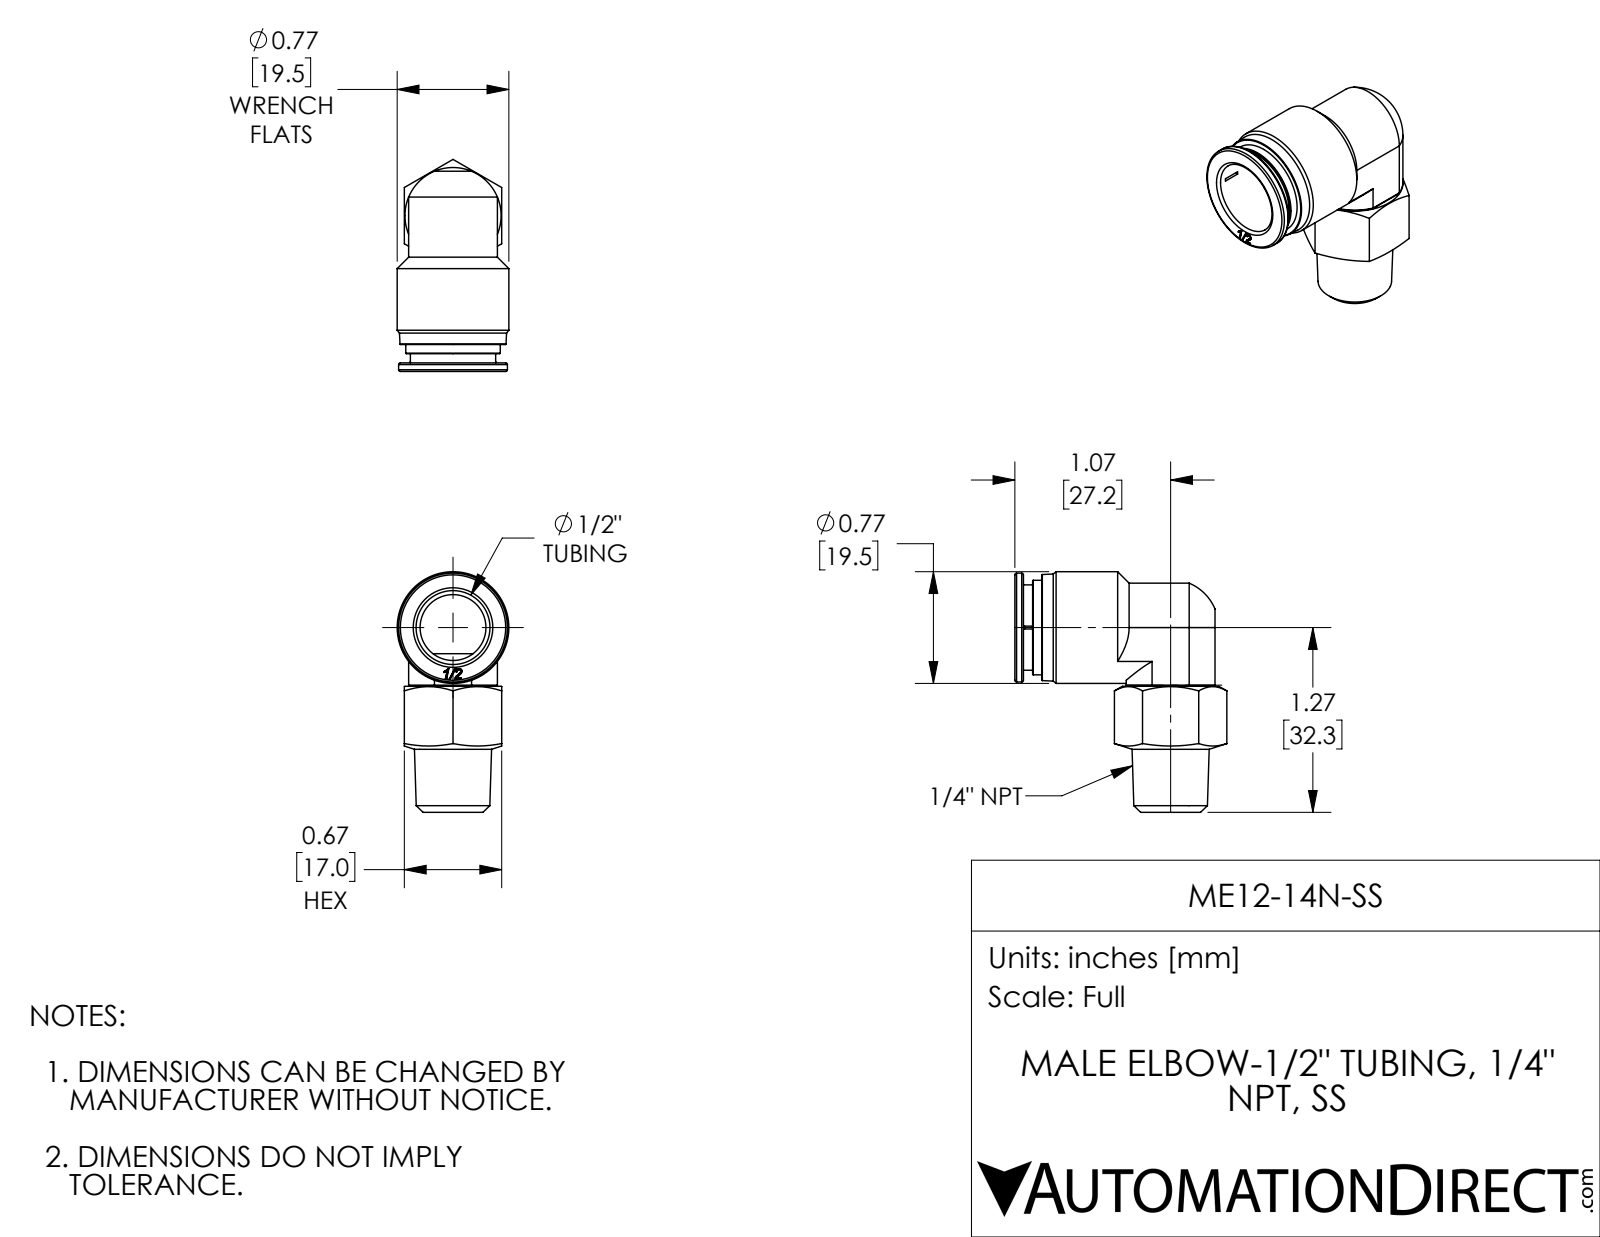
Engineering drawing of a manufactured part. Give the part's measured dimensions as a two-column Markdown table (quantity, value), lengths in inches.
| quantity | value |
| --- | --- |
| part name | ME12-14N-SS |
| STEP written by | SolidWorks 2017 (AUTOMOTIVE_DESIGN) |
| units | inches |
| bodies | 2 solids, 128 faces (43 planar, 31 cylindrical, 54 other) |
| overall size | 1.654 × 1.457 × 0.768 |
| volume | 0.502 in³ |
| surface area | 10.04 in² |
| round holes (diameter × count) | 0.276 × 1, 0.356 × 1, 0.453 × 1, 0.508 × 1, 0.594 × 1 |
| round bosses / shafts (diameter × count) | 0.768 × 1, 0.748 × 1, 0.65 × 1, 0.587 × 1, 0.354 × 1 |
| partial cylindrical surfaces (radius × count) | 0.008 × 4, 0.305 × 1, 0.331 × 1 |
| main face-to-face distances | 0.669, 0.03, 0.64, 0.61, 0.059, 1.376, 1.317, 0.185, 0.126, 1.191 |
